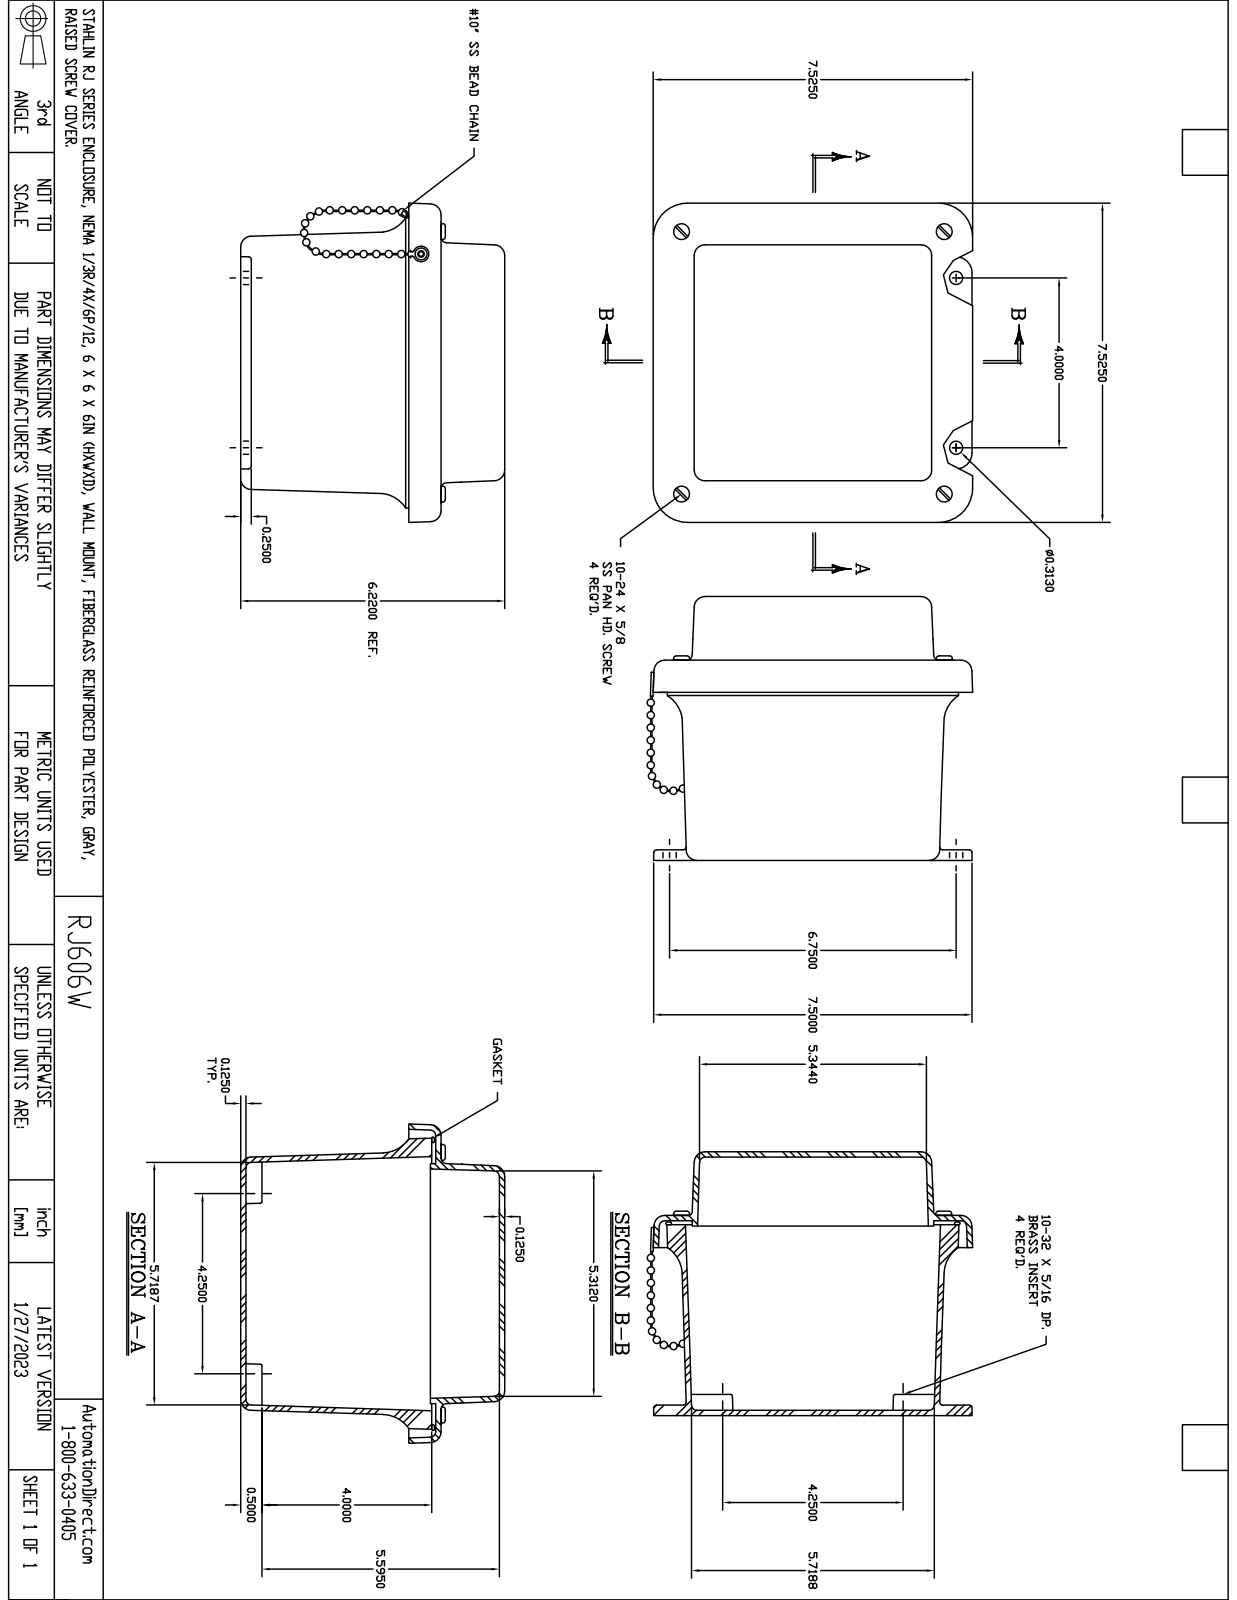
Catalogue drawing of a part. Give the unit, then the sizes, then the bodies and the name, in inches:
Units: inches
Overall size (bounding box): 8.065 × 7.723 × 6.324
Round holes (diameter × count): ⌀0.152 ×5, ⌀0.145 ×4, ⌀0.156 ×4, ⌀0.218 ×4, ⌀0.14 ×3, ⌀0.187 ×2, ⌀0.126 ×1
Round bosses / shafts (diameter × count): ⌀0.27 ×8, ⌀0.19 ×4, ⌀0.156 ×4, ⌀0.375 ×2, ⌀0.25 ×2, ⌀0.125 ×2, ⌀0.283 ×1
Partial cylindrical surfaces — rounded edges, fillets, slot ends (radius × count): R0.031 ×20, R0.125 ×16, R0.25 ×16, R0.063 ×4, R0.2 ×4, R0.311 ×4, R0.313 ×4, R0.375 ×4
Main face-to-face distances: 0.125, 6.199, 4.699, 1.5, 0.125, 6.074, 6.324, 4.574, 1.625, 4.824
Hole centre spacings: 5.308, 1.37, 4.25, 6.187, 7.38, 6.01, 8.75, 4
Volume: 40.08 in³ · Surface area: 553.7 in²
Bodies: 45 solids, 939 faces (208 planar, 301 cylindrical, 430 other)
Part name (STEP PRODUCT): MR606W
STEP written by: SolidWorks 2018 (AUTOMOTIVE_DESIGN)
